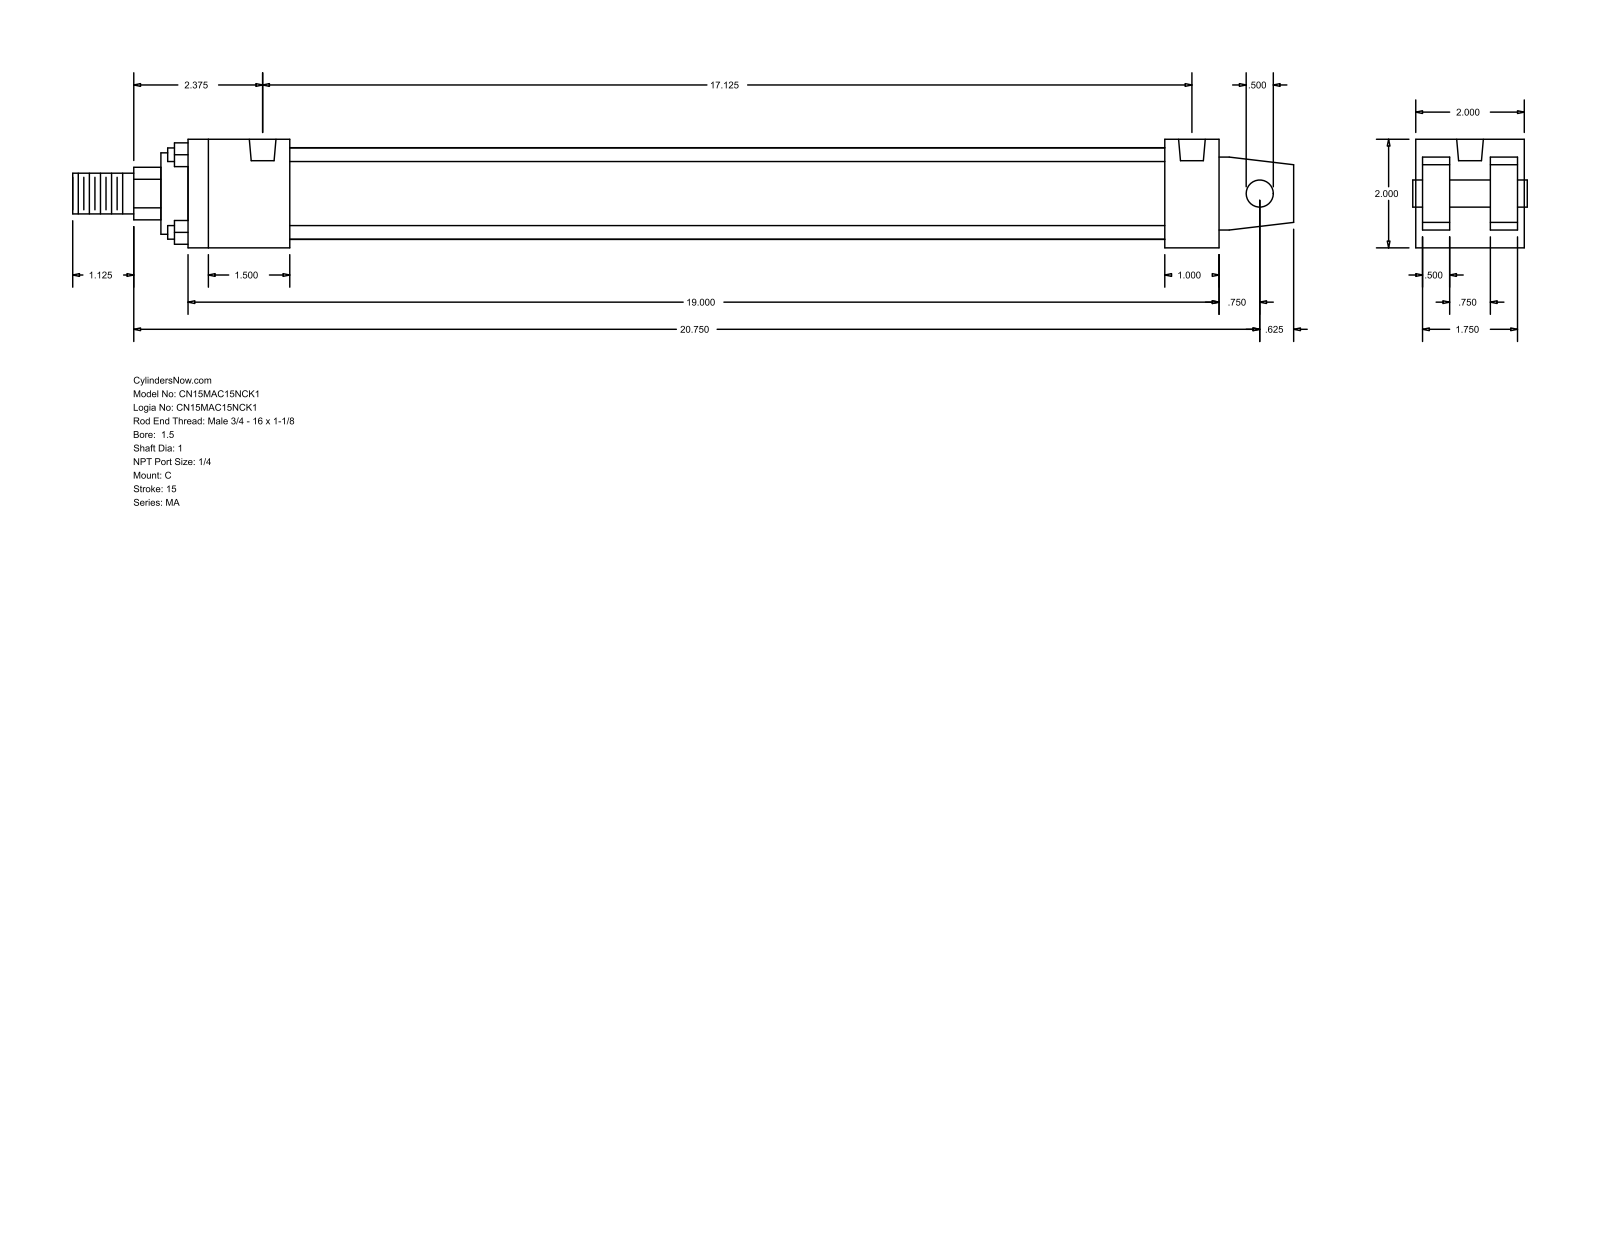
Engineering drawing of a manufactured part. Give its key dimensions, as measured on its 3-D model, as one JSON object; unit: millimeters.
{"part_name": "MA_C__0150_1", "step_written_by": "GSSL Pune (CONFIG_CONTROL_DESIGN)", "units": "millimeters", "bodies": {"solids": 0, "faces": 103, "planar": 76, "cylindrical": 27, "other": 0}, "overall_size": [571.5, 50.8, 50.8], "round_holes": [[7.94, 4], [12.49, 2]], "round_bosses_or_shafts": [[6.35, 4], [42.93, 1], [38.1, 1], [25.4, 1], [19.05, 1], [12.7, 1]], "partial_cylinders_radius": [[12.29, 1]], "face_to_face_distances": [50.8, 47.63, 12.7, 3.17, 15.87, 34.93, 31.76, 482.6, 25.4, 457.2], "hole_center_spacings": [434.97]}
